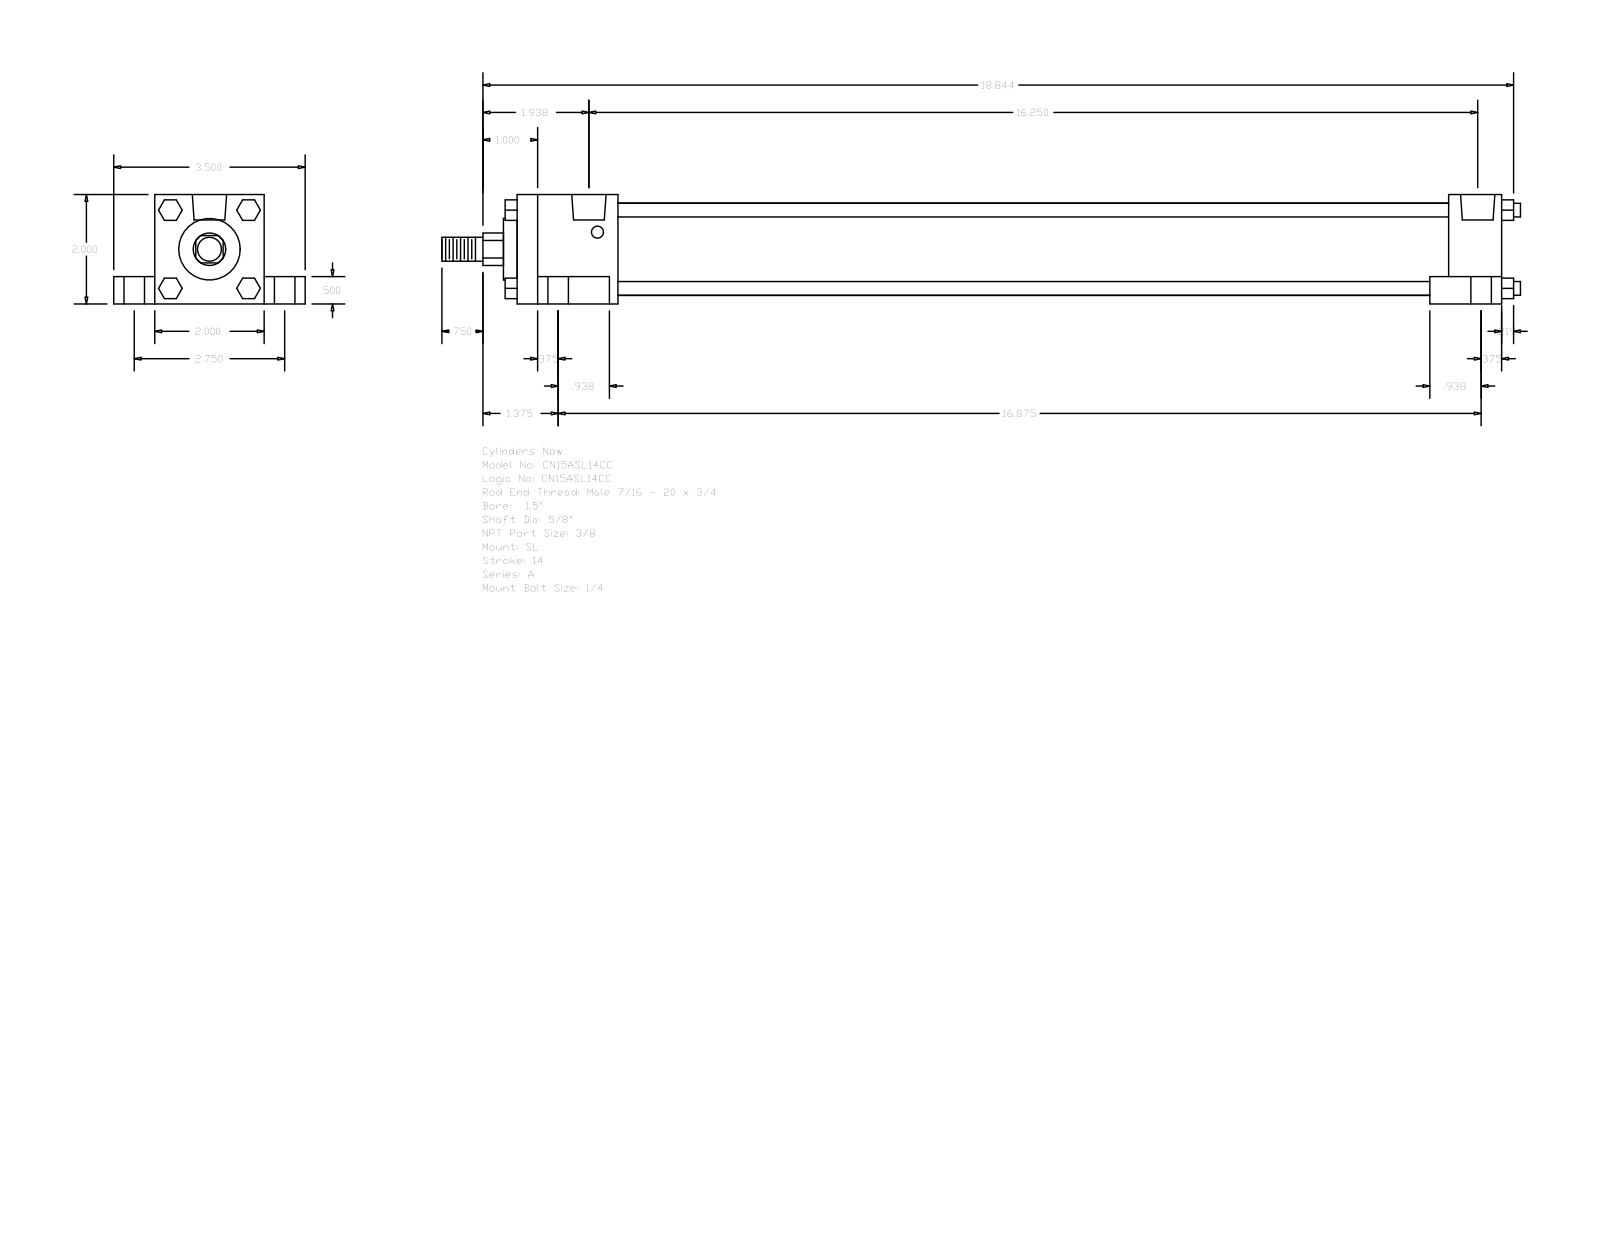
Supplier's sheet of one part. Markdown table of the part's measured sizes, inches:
| quantity | value |
| --- | --- |
| part name | A_SL__0150_0.625 |
| STEP written by | GSSL Pune (CONFIG_CONTROL_DESIGN) |
| units | inches |
| bodies | 0 solids, 148 faces (112 planar, 36 cylindrical, 0 other) |
| overall size | 19.719 × 3.5 × 2 |
| round holes (diameter × count) | 0.219 × 4, 0.375 × 4, 0.625 × 4, 0.627 × 2 |
| round bosses / shafts (diameter × count) | 0.25 × 4, 1.69 × 1, 1.125 × 1, 0.625 × 1, 0.437 × 1 |
| partial cylindrical surfaces (radius × count) | 0.297 × 1 |
| main face-to-face distances | 2, 0.75, 1.5, 0.5, 2.75, 18, 0.375, 17.031, 0.969, 1.844 |
| hole center spacings | 0.156, 1.376, 1.392, 1.485, 1.552, 2.75, 15.937, 16.094 |
